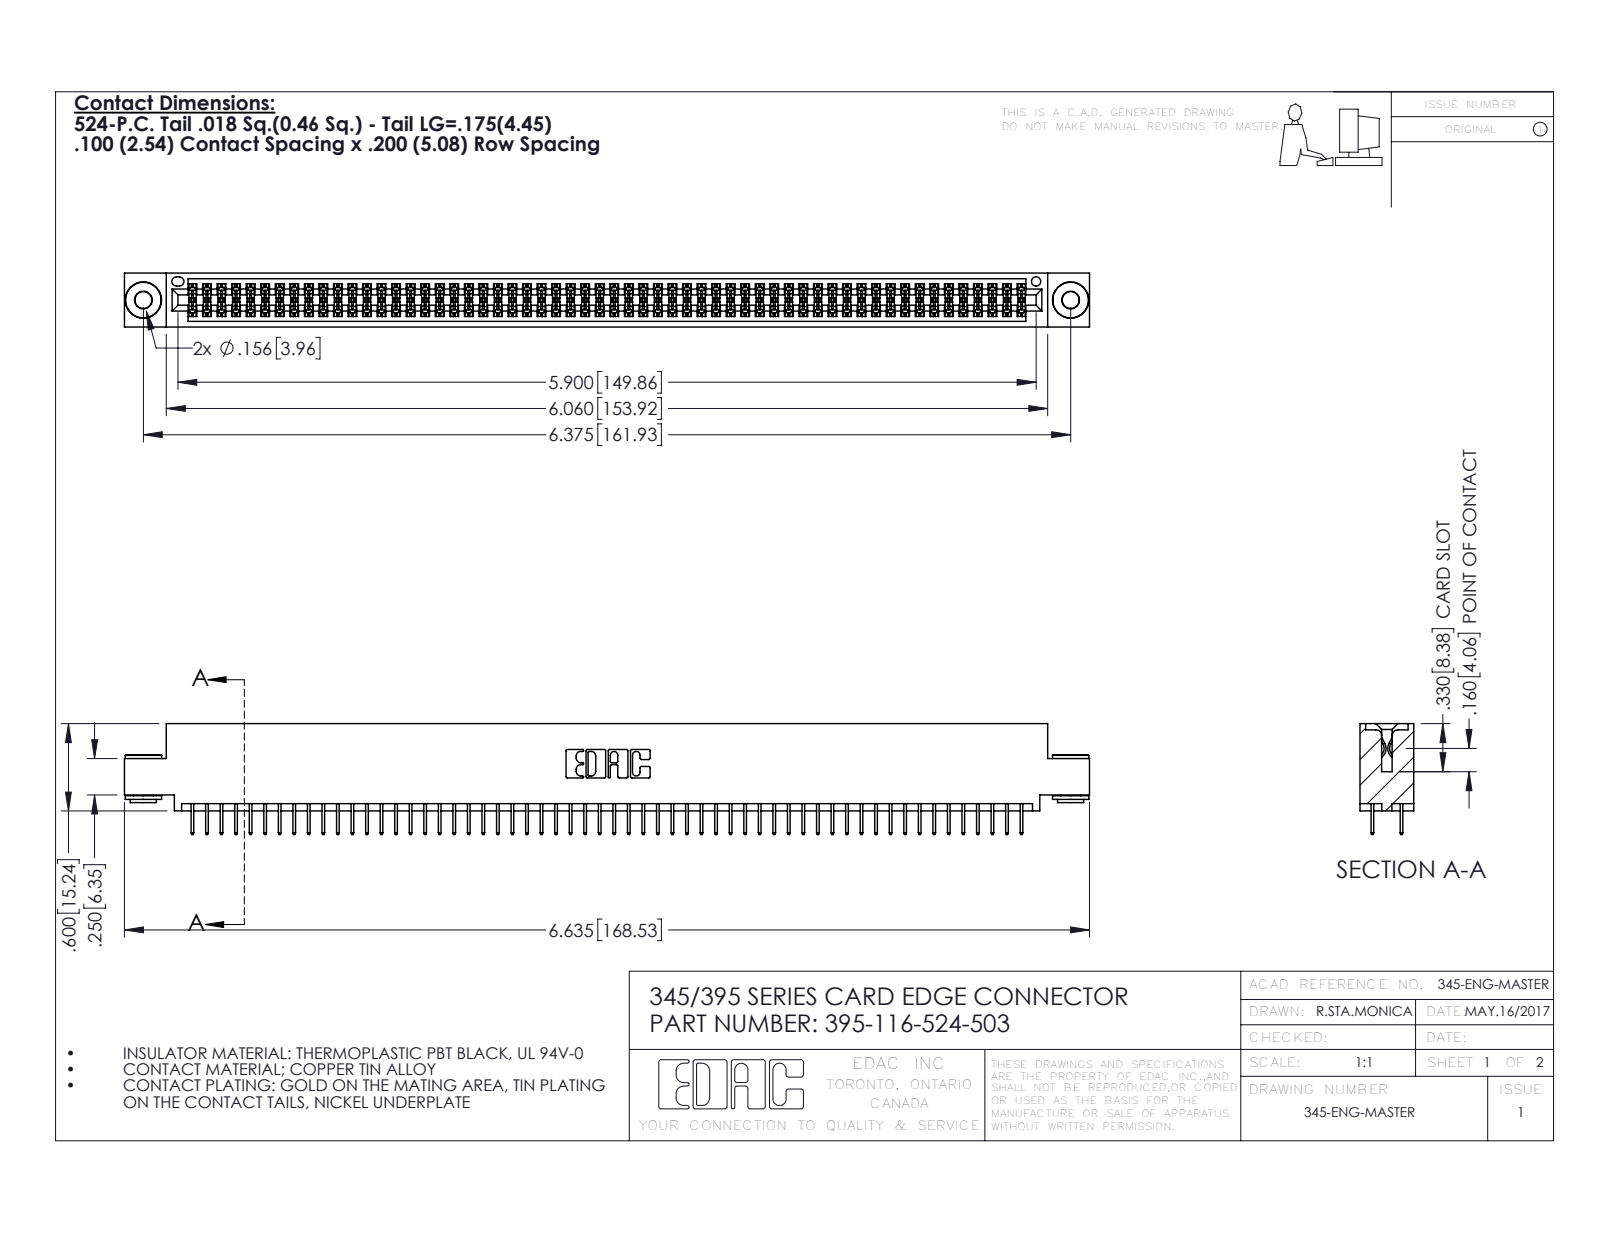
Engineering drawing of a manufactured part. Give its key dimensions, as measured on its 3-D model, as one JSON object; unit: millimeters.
{"part_name": "345 Part_0.110 Offset - 0.156 Dia-TH; 395-116-524-503; 345-250-002_345-250-002-102; 345-292-001_345-293-124", "step_written_by": "SolidWorks 2016 (CONFIG_CONTROL_DESIGN)", "units": "millimeters", "bodies": {"solids": 119, "faces": 6432, "planar": 4618, "cylindrical": 1806, "other": 8}, "overall_size": [168.5, 19.4, 9.4], "volume_mm3": 16300, "surface_area_mm2": 24230, "round_holes": [[2.9, 2], [4, 2], [1.6, 1]], "round_bosses_or_shafts": [[6.4, 2], [4.6, 2], [3.5, 2]], "partial_cylinders_radius": [[0.2, 174], [0.3, 22], [0.2, 6], [0.8, 6], [0.7, 3], [0.4, 2], [0.5, 2], [0.6, 2]], "face_to_face_distances": [1.8, 7.6, 5.1, 9.4, 0.6, 2.5, 6.9, 5.7, 1.8, 4.4], "hole_center_spacings": [6.9, 155.9, 161.9]}
